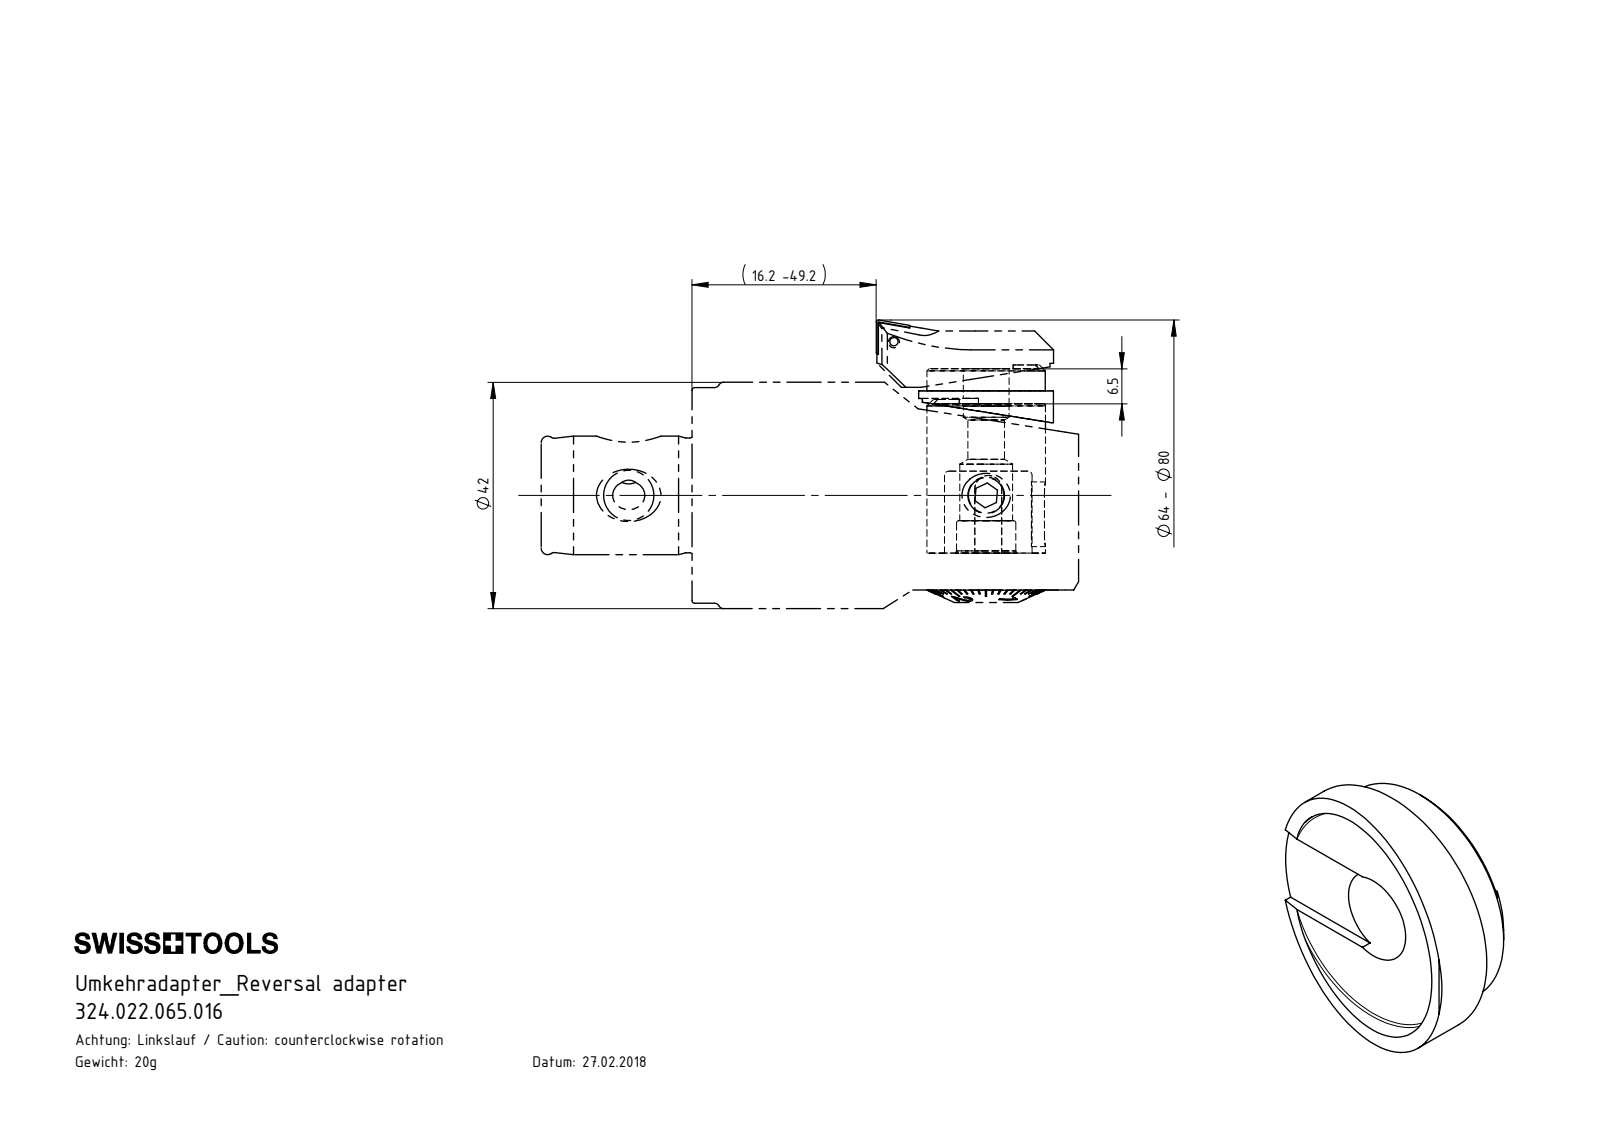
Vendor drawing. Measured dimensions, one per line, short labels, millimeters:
name: 324.022.065.016; F42-U00.001.006_B
written by: SolidWorks 2017 (CONFIG_CONTROL_DESIGN)
unit: mm
bodies: 1 solid, 28 faces (12 planar, 11 cylindrical, 5 other)
size: 25 × 25 × 10.7
volume: 2 498 mm³; area: 1 746 mm²
holes: 1× ⌀8.5, 1× ⌀22
bosses: 1× ⌀25
rounds: 2× R0.5
face distances: 6.5, 4.1, 2.4, 5.5, 1.4, 1, 0.7, 4.8, 6.2, 7.2
